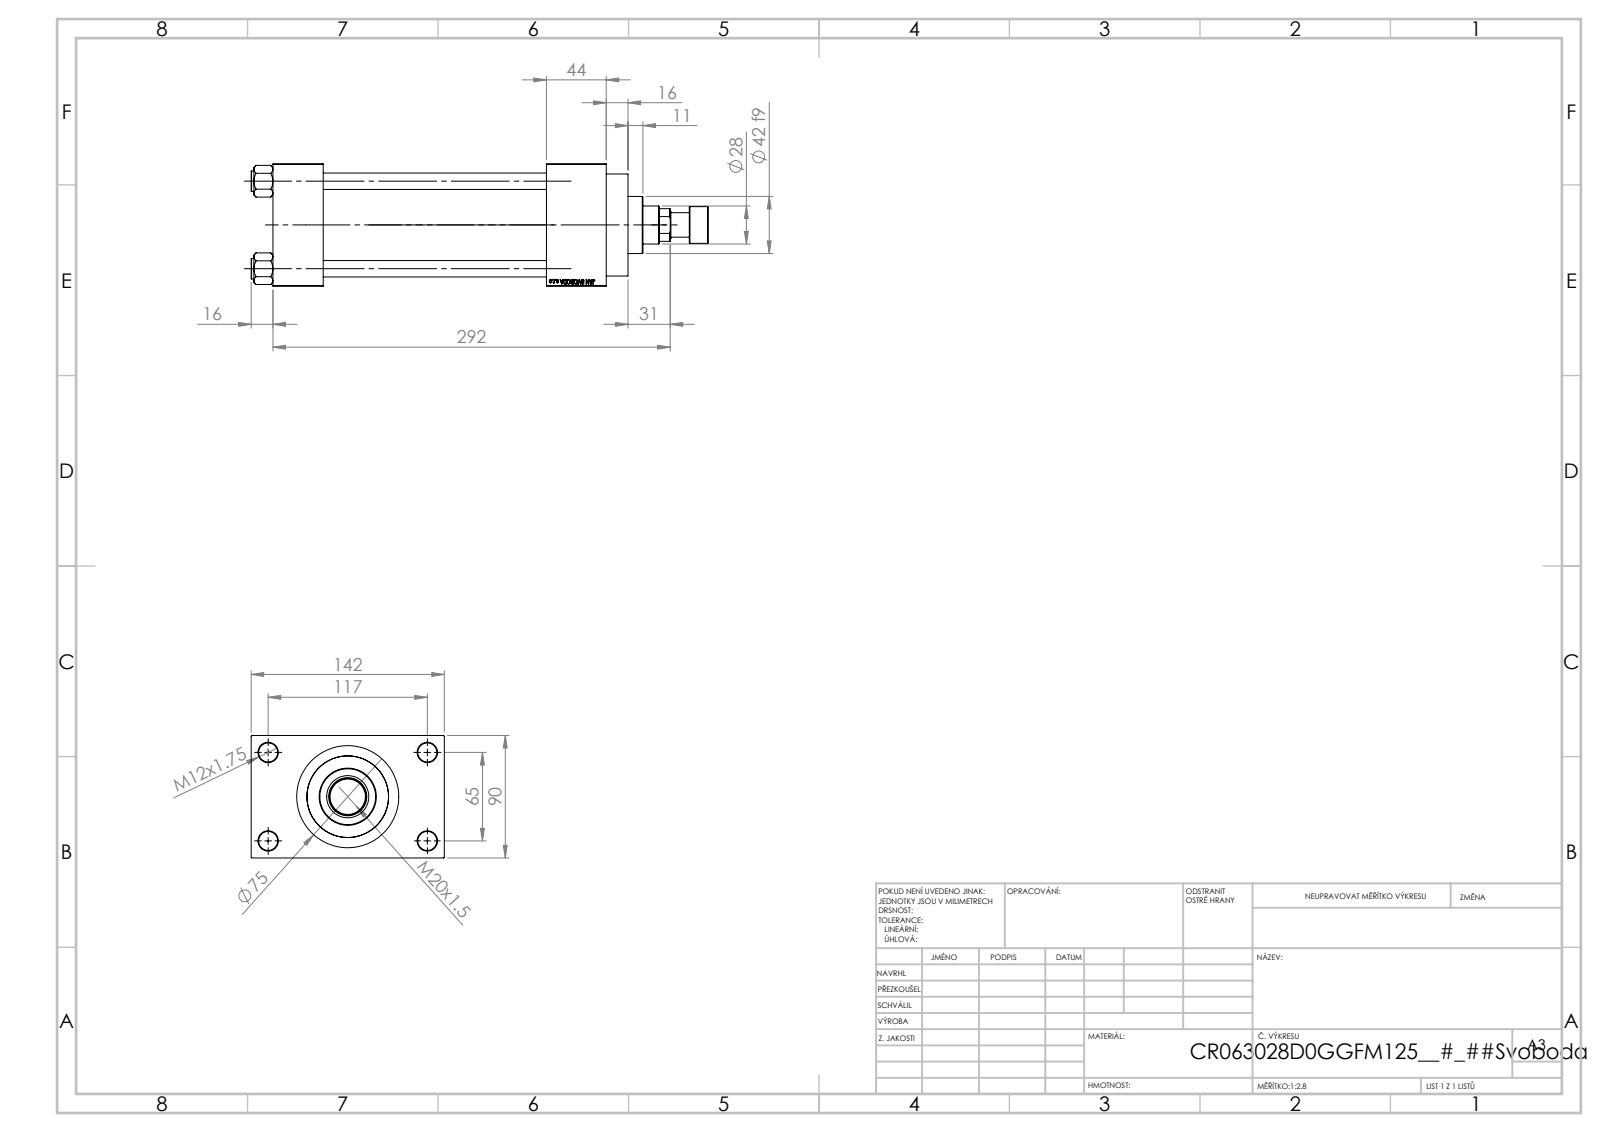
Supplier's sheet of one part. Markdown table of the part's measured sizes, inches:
| quantity | value |
| --- | --- |
| part name | V215CR_VCP_D; V215CR_D_TYCINKA; V215CR_D_Body; NUT_M5_D (+2 more) |
| STEP written by | SolidWorks 2019 (CONFIG_CONTROL_DESIGN) |
| units | inches |
| bodies | 12 solids, 1118 faces (501 planar, 93 cylindrical, 524 other) |
| overall size | 13.228 × 5.591 × 3.543 |
| volume | 78.96 in³ |
| surface area | 419.2 in² |
| round holes (diameter × count) | 0.472 × 4, 0.551 × 4, 0.276 × 2, 0.825 × 2, 1.181 × 2, 0.728 × 1, 1.102 × 1, 1.22 × 1, 1.969 × 1, 2.362 × 1, 2.48 × 1 |
| round bosses / shafts (diameter × count) | 0.591 × 4, 2.953 × 1, 2.717 × 1, 1.654 × 1, 1.063 × 1, 0.709 × 1 |
| main face-to-face distances | 3.543, 6.457, 1.457, 7.913, 8.189, 9.646, 1.732, 1.024, 4.567, 5.591 |
| hole center spacings | 1.037, 1.79, 2.531, 2.635, 2.748, 3.569, 4.383, 2.559 |
